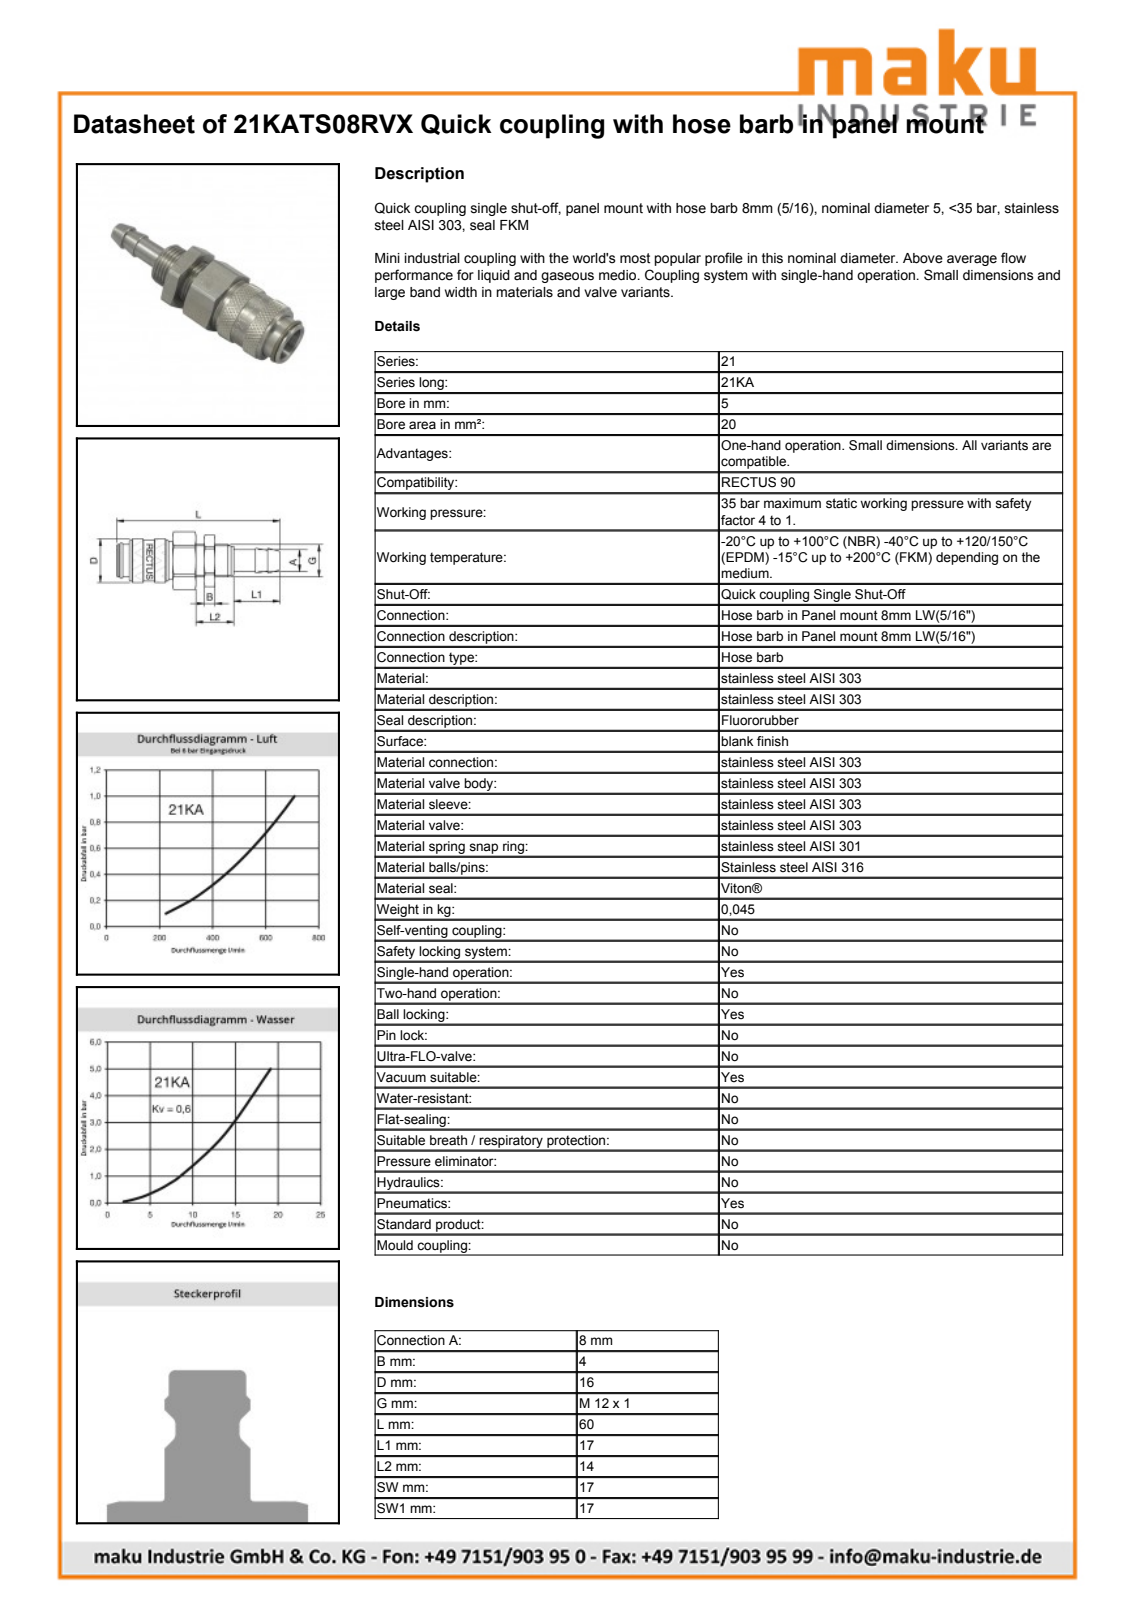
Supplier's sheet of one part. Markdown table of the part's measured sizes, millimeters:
| quantity | value |
| --- | --- |
| part name | D104304 |
| STEP written by | Autodesk Inventor 2013 (AUTOMOTIVE_DESIGN) |
| units | millimeters |
| bodies | 2 solids, 531 faces (208 planar, 70 cylindrical, 253 other) |
| overall size | 60.15 × 19.09 × 18.21 |
| volume | 8 328 mm³ |
| surface area | 4 767 mm² |
| round holes (diameter × count) | 12.15 × 1, 14 × 1 |
| round bosses / shafts (diameter × count) | 16.15 × 1, 15.1 × 1, 12 × 1, 11.4 × 1, 11.24 × 1, 11.15 × 1, 10.6 × 1, 8.05 × 1 |
| partial cylindrical surfaces (radius × count) | 7.45 × 1, 9.57 × 1 |
| main face-to-face distances | 17, 29.15, 37.33, 8.18, 33.33, 4.18, 4, 20.6, 8.55, 12.73 |
